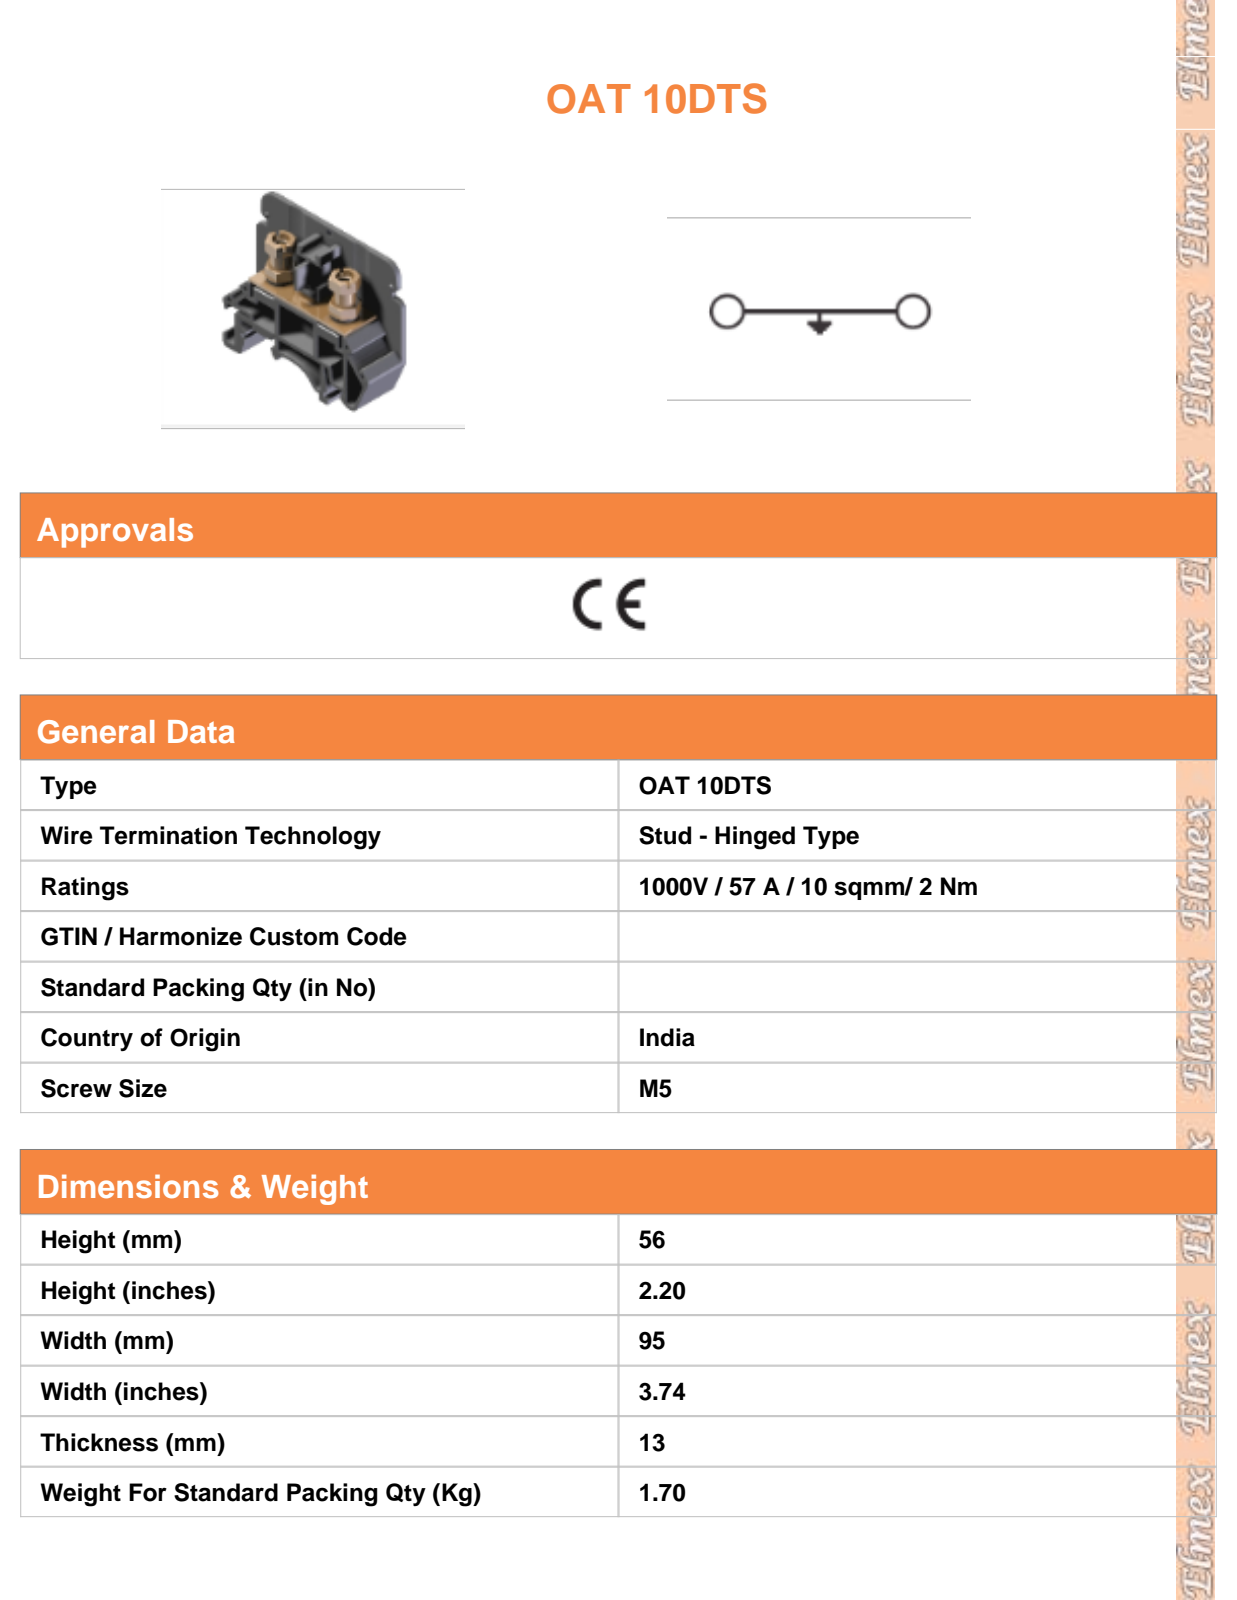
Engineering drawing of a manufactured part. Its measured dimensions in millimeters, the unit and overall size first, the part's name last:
Units: millimetres
Overall size (bounding box): 95 × 63.5 × 13.02
Round holes (diameter × count): ⌀2 ×8, ⌀2.46 ×4, ⌀2.75 ×2, ⌀3.2 ×2, ⌀4 ×2, ⌀4.13 ×2, ⌀5.2 ×2, ⌀5.5 ×2, ⌀5.6 ×2, ⌀5.7 ×2, ⌀6 ×2, ⌀8.3 ×2
Round bosses / shafts (diameter × count): ⌀9 ×3, ⌀8 ×2, ⌀7.3 ×2, ⌀7.2 ×2, ⌀6.5 ×2, ⌀5.5 ×2, ⌀5 ×2, ⌀4.8 ×2
Partial cylindrical surfaces — rounded edges, fillets, slot ends (radius × count): R0.5 ×78, R0.2 ×23, R1 ×21, R0.25 ×19, R0.3 ×19, R0.75 ×9, R0.4 ×8, R0.43 ×8
Main face-to-face distances: 1.5, 1, 7.1, 2, 3, 11.5, 13, 8.3, 2.5, 6.25
Hole centre spacings: 7.18, 7.28, 19.4, 36.68, 36.78, 42.21, 48.9, 4.48
Volume: 22 932 mm³ · Surface area: 36 173 mm²
Bodies: 2 solids, 1315 faces (842 planar, 327 cylindrical, 146 other)
STEP written by: ST-DEVELOPER v16.7 (AUTOMOTIVE_DESIGN)
